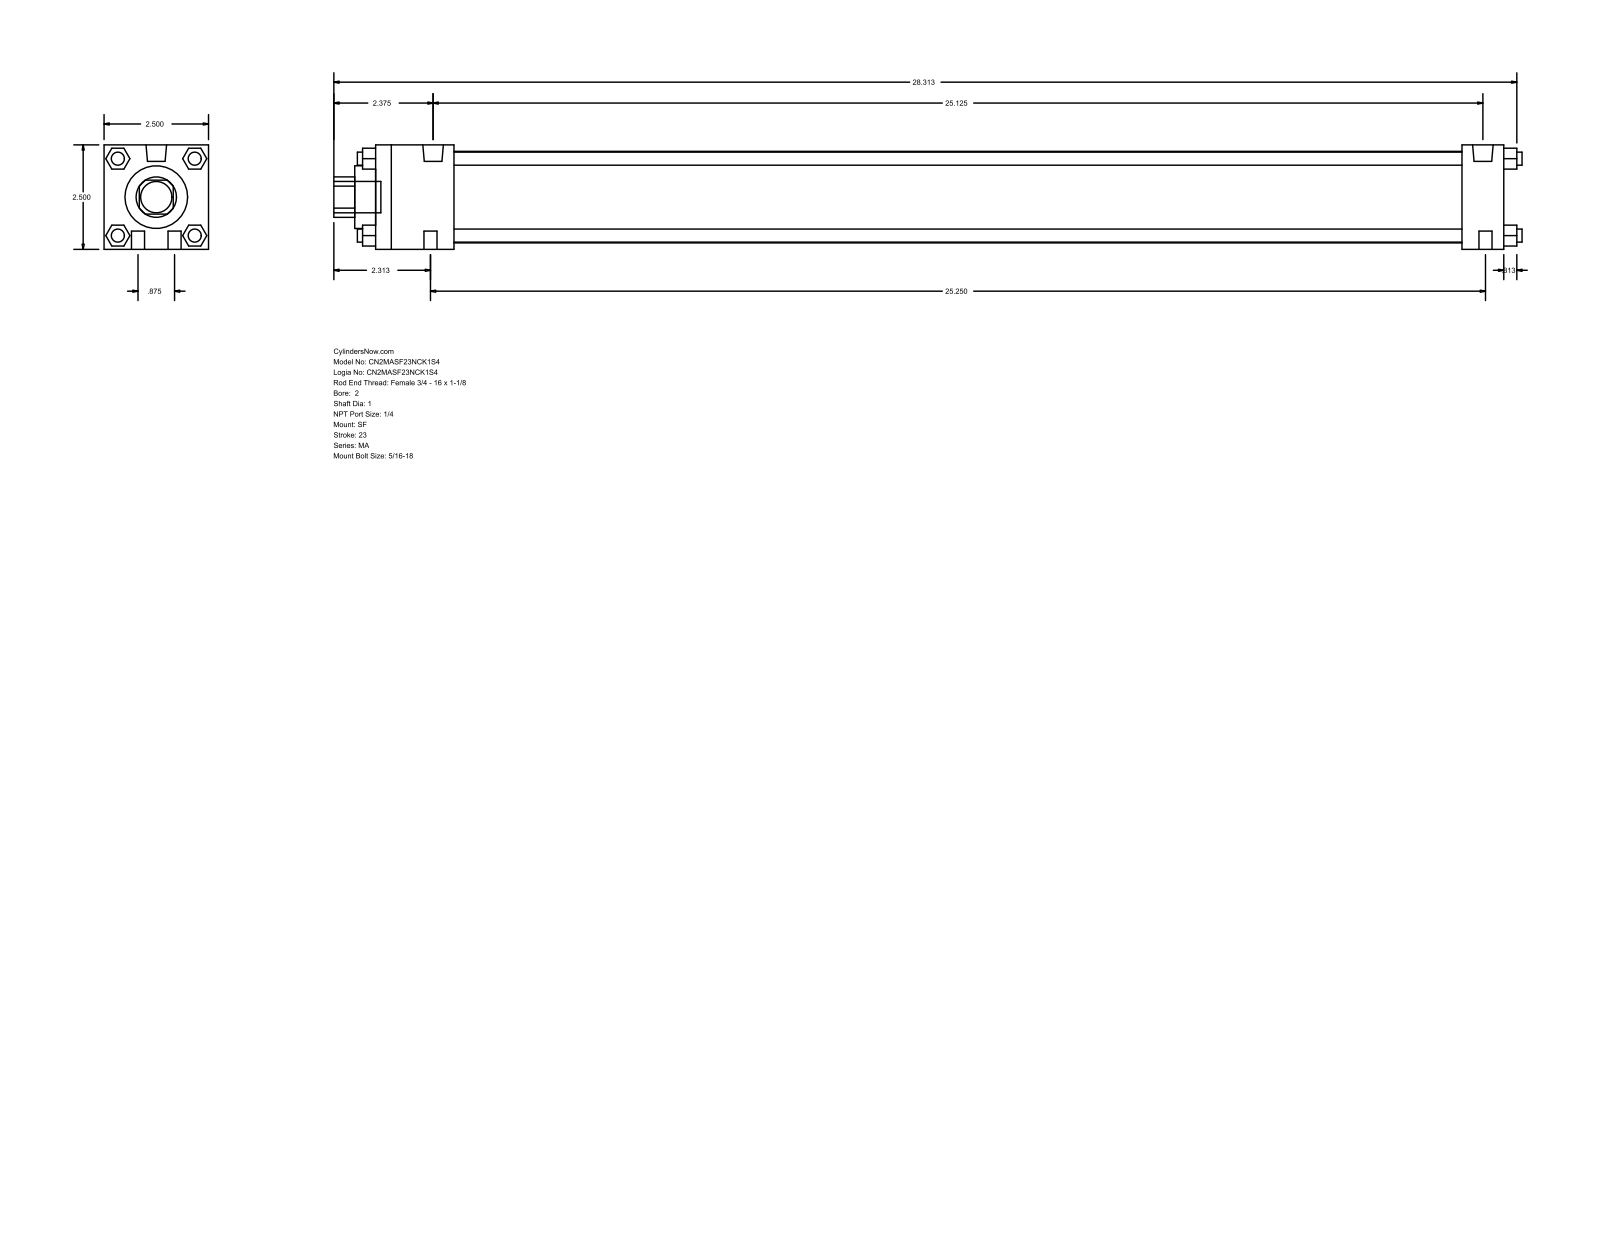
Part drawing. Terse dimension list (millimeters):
name: MA_SF__0200_1
written by: GSSL Pune (CONFIG_CONTROL_DESIGN)
unit: mm
bodies: 0 solids, 124 faces (94 planar, 30 cylindrical, 0 other)
size: 722.31 × 63.5 × 63.5
holes: 1× ⌀25.4, 1× ⌀38.1, 1× ⌀55.63
bosses: 10× ⌀7.94, 2× ⌀12.49, 1× ⌀19.05
rounds: 1× R12.29
face distances: 63.5, 685.8, 12.7, 25.4, 660.4, 47.63, 612.77, 638.17, 23.37, 40.47
